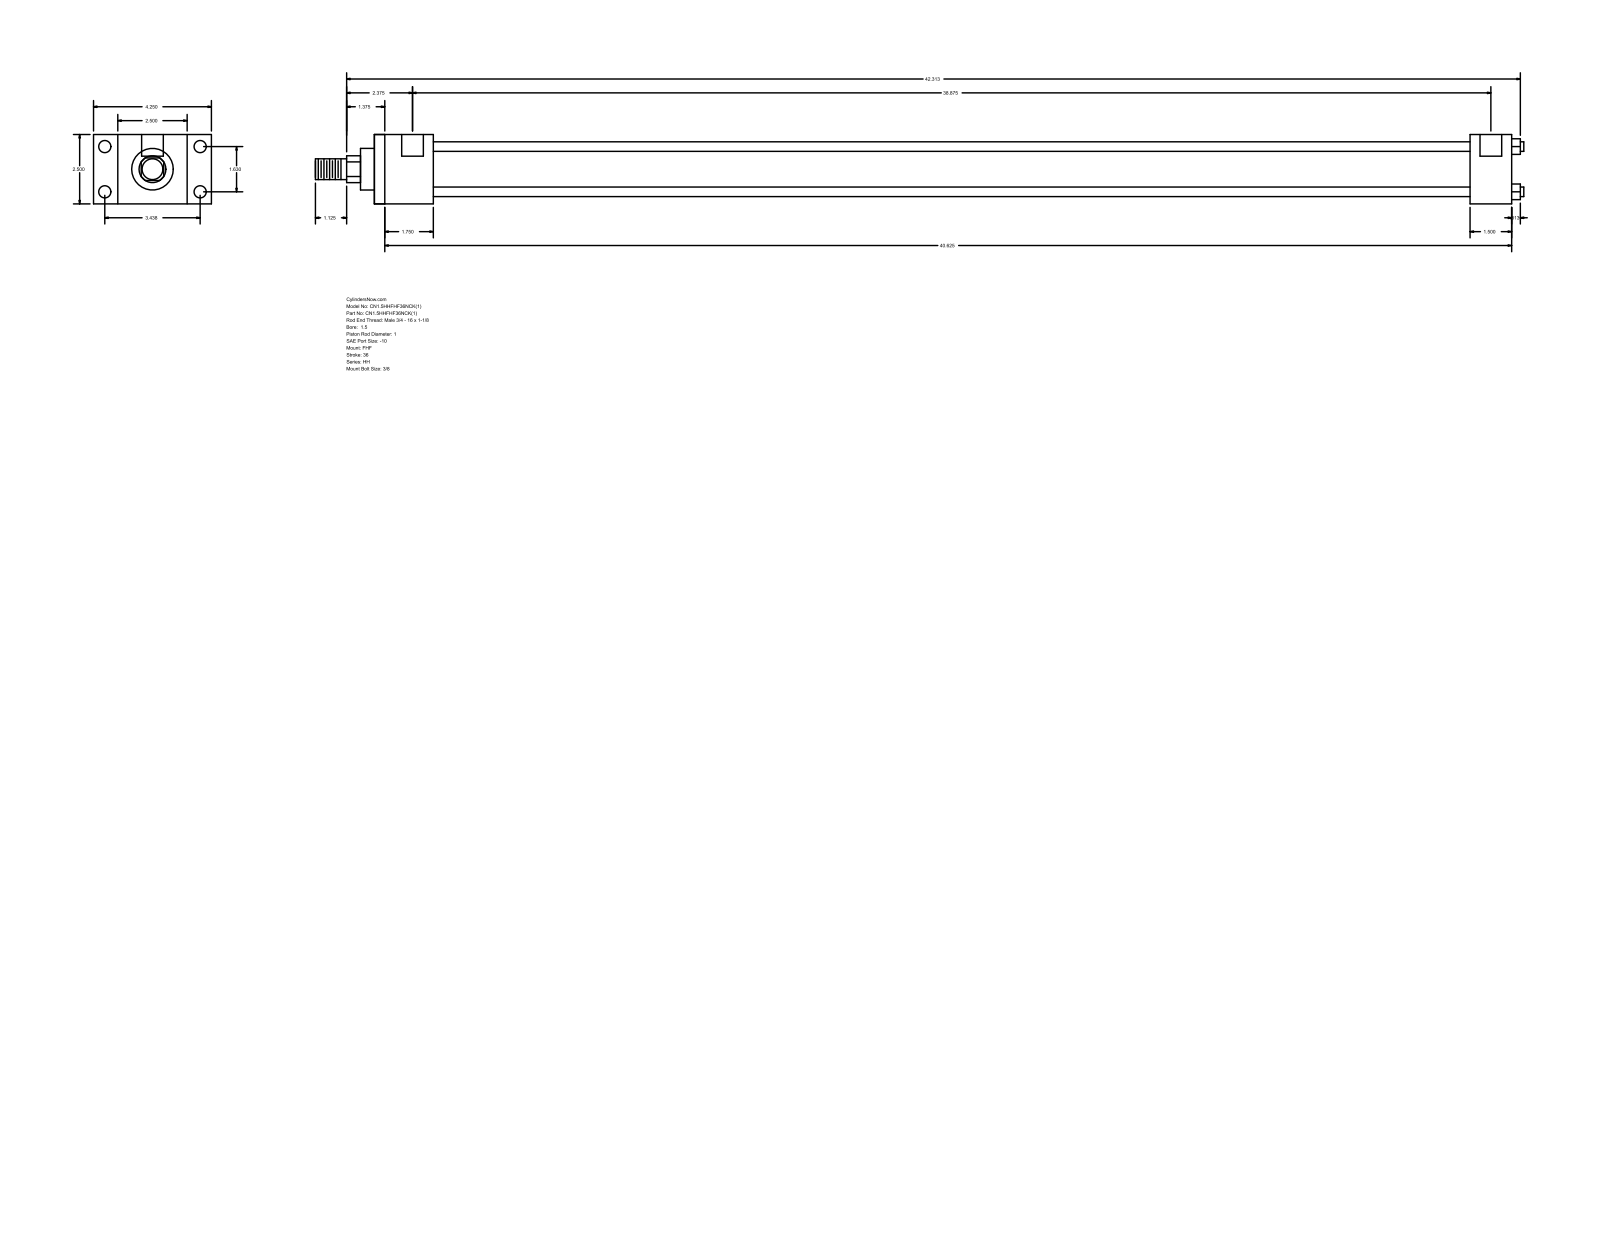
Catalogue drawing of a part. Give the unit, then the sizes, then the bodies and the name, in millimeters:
Units: millimetres
Overall size (bounding box): 1106.49 × 107.95 × 63.5
Round holes (diameter × count): ⌀5.56 ×4, ⌀11.13 ×4, ⌀19.84 ×2
Round bosses / shafts (diameter × count): ⌀8.76 ×4, ⌀44.45 ×1, ⌀38.1 ×1, ⌀25.4 ×1, ⌀19.05 ×1
Partial cylindrical surfaces — rounded edges, fillets, slot ends (radius × count): R12.29 ×1
Main face-to-face distances: 63.5, 22.23, 85.73, 53.98, 107.96, 1041.4, 987.42, 38.1, 1003.3, 949.32
Hole centre spacings: 1.59, 41.4, 87.32, 96.64, 989.01, 990.6, 987.42
Bodies: 0 solids, 88 faces (60 planar, 28 cylindrical, 0 other)
Part name (STEP PRODUCT): HH_FHF__0150_1
STEP written by: GSSL Pune (CONFIG_CONTROL_DESIGN)
